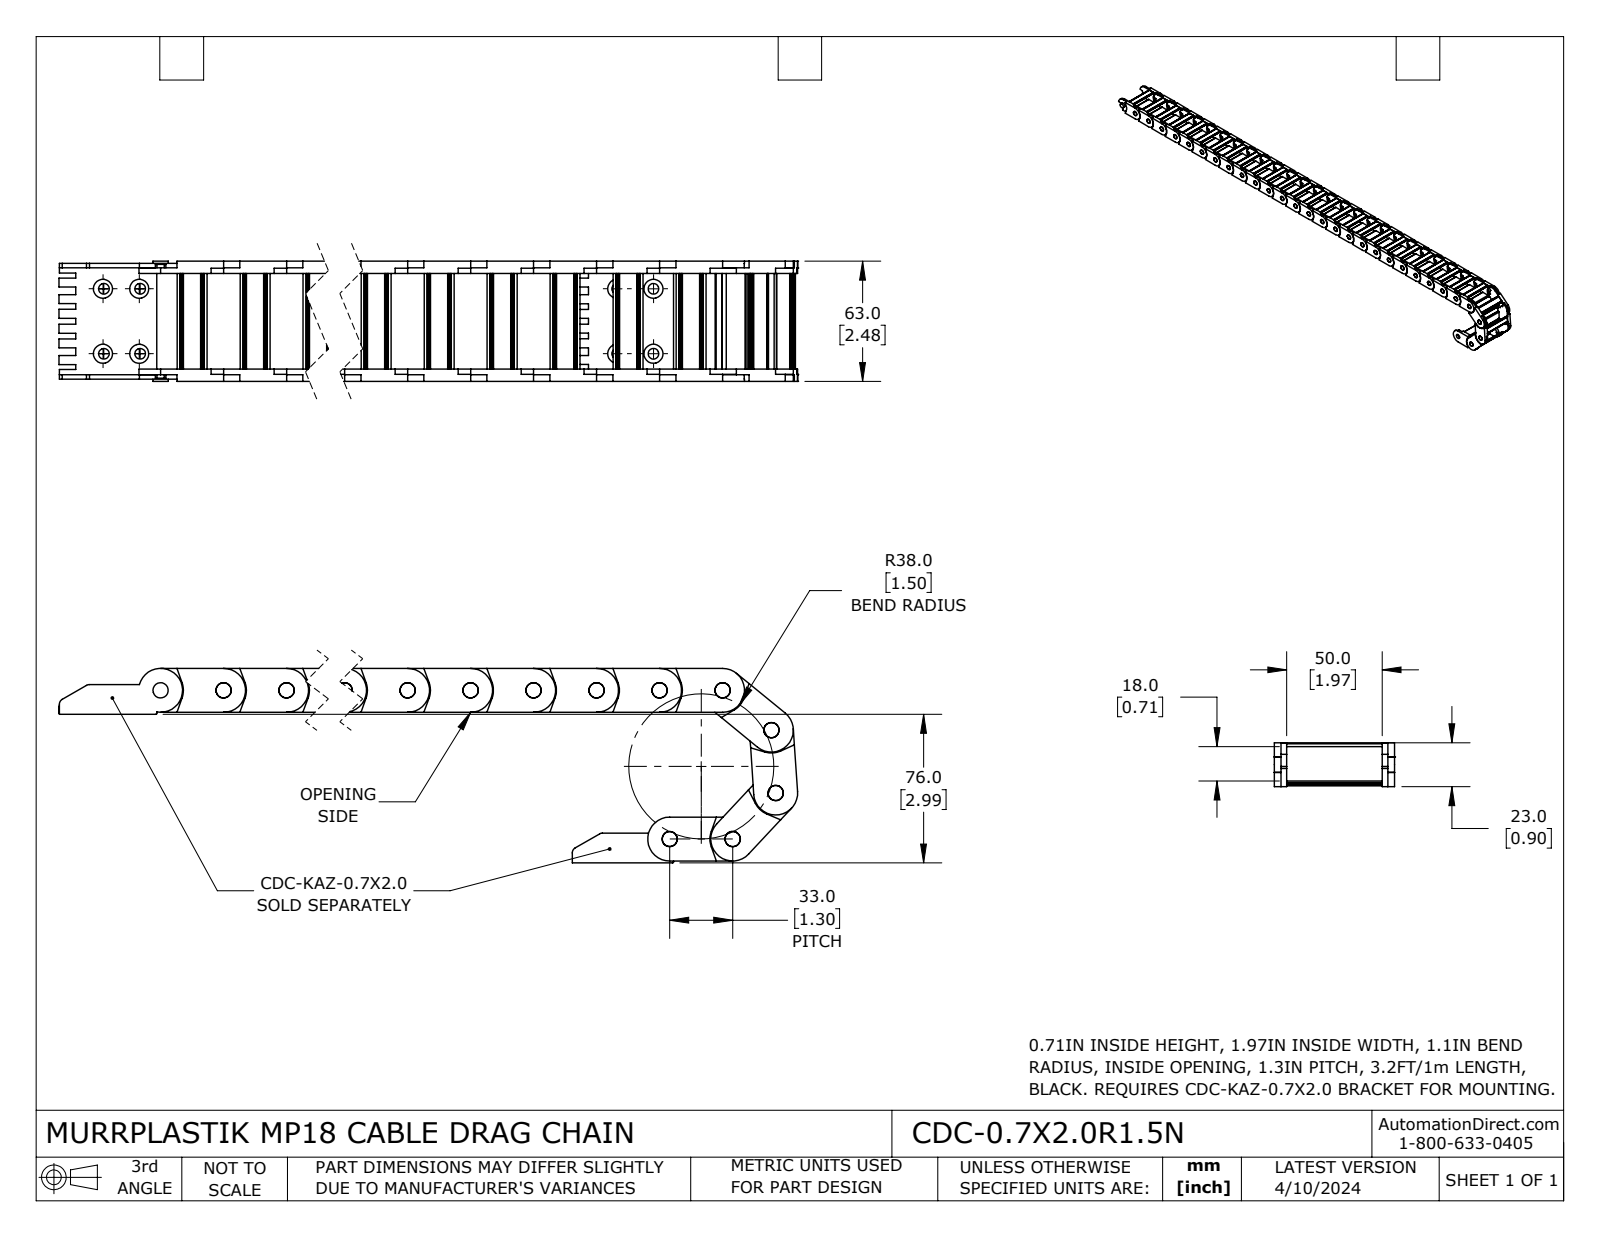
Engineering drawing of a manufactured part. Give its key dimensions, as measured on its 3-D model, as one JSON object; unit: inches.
{"part_name": "CDC-0.7X2.0R1.5N", "step_written_by": "SolidWorks 2023 (CONFIG_CONTROL_DESIGN)", "units": "inches", "bodies": {"solids": 30, "faces": 2370, "planar": 1110, "cylindrical": 1260, "other": 0}, "overall_size": [35.773, 3.972, 2.48], "volume_in3": 21.06, "surface_area_in2": 414.1, "round_holes": [[0.315, 30]], "round_bosses_or_shafts": [[0.315, 1]], "partial_cylinders_radius": [[0.02, 120], [0.059, 120], [0.008, 60], [0.012, 60], [0.453, 31], [0.47, 31], [0.197, 30], [0.215, 30]], "face_to_face_distances": [0.256, 2.224, 2.48, 0.079, 0.138, 2.343, 0.118, 2.087, 0.146, 2.335], "hole_center_spacings": [1.299, 2.598, 3.898, 5.197, 6.496, 7.795, 9.094, 10.394]}
